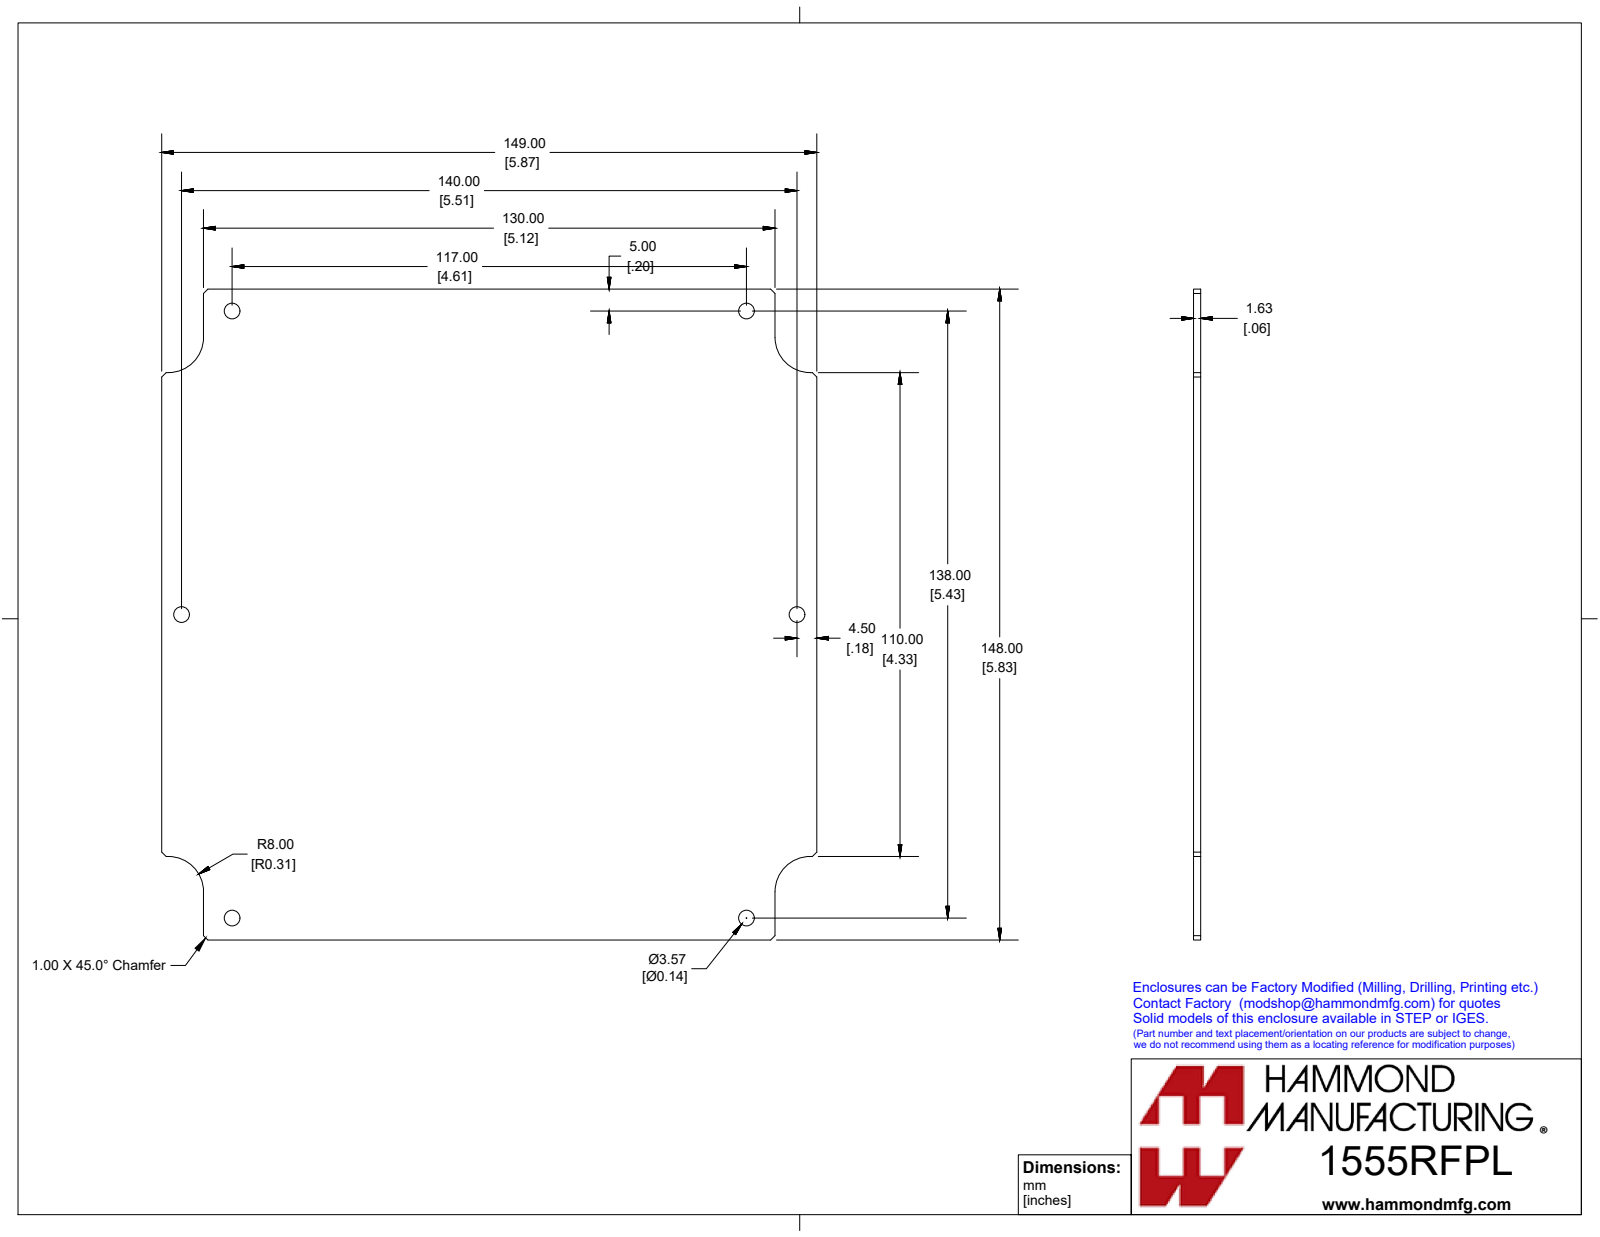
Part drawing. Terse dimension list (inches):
name: 1555RFPL
written by: SolidWorks 2019 (CONFIG_CONTROL_DESIGN)
unit: in
bodies: 1 solid, 32 faces (22 planar, 10 cylindrical, 0 other)
size: 5.866 × 5.827 × 0.064
volume: 2.115 in³; area: 67.71 in²
holes: 6× ⌀0.141
rounds: 4× R0.315
face distances: 0.064, 5.827, 5.866, 0.374, 5.492, 5.118, 0.265, 7.418, 7.154, 7.683
hole spacings: 2.754, 5.742, 4.606, 5.433, 7.123, 5.512
